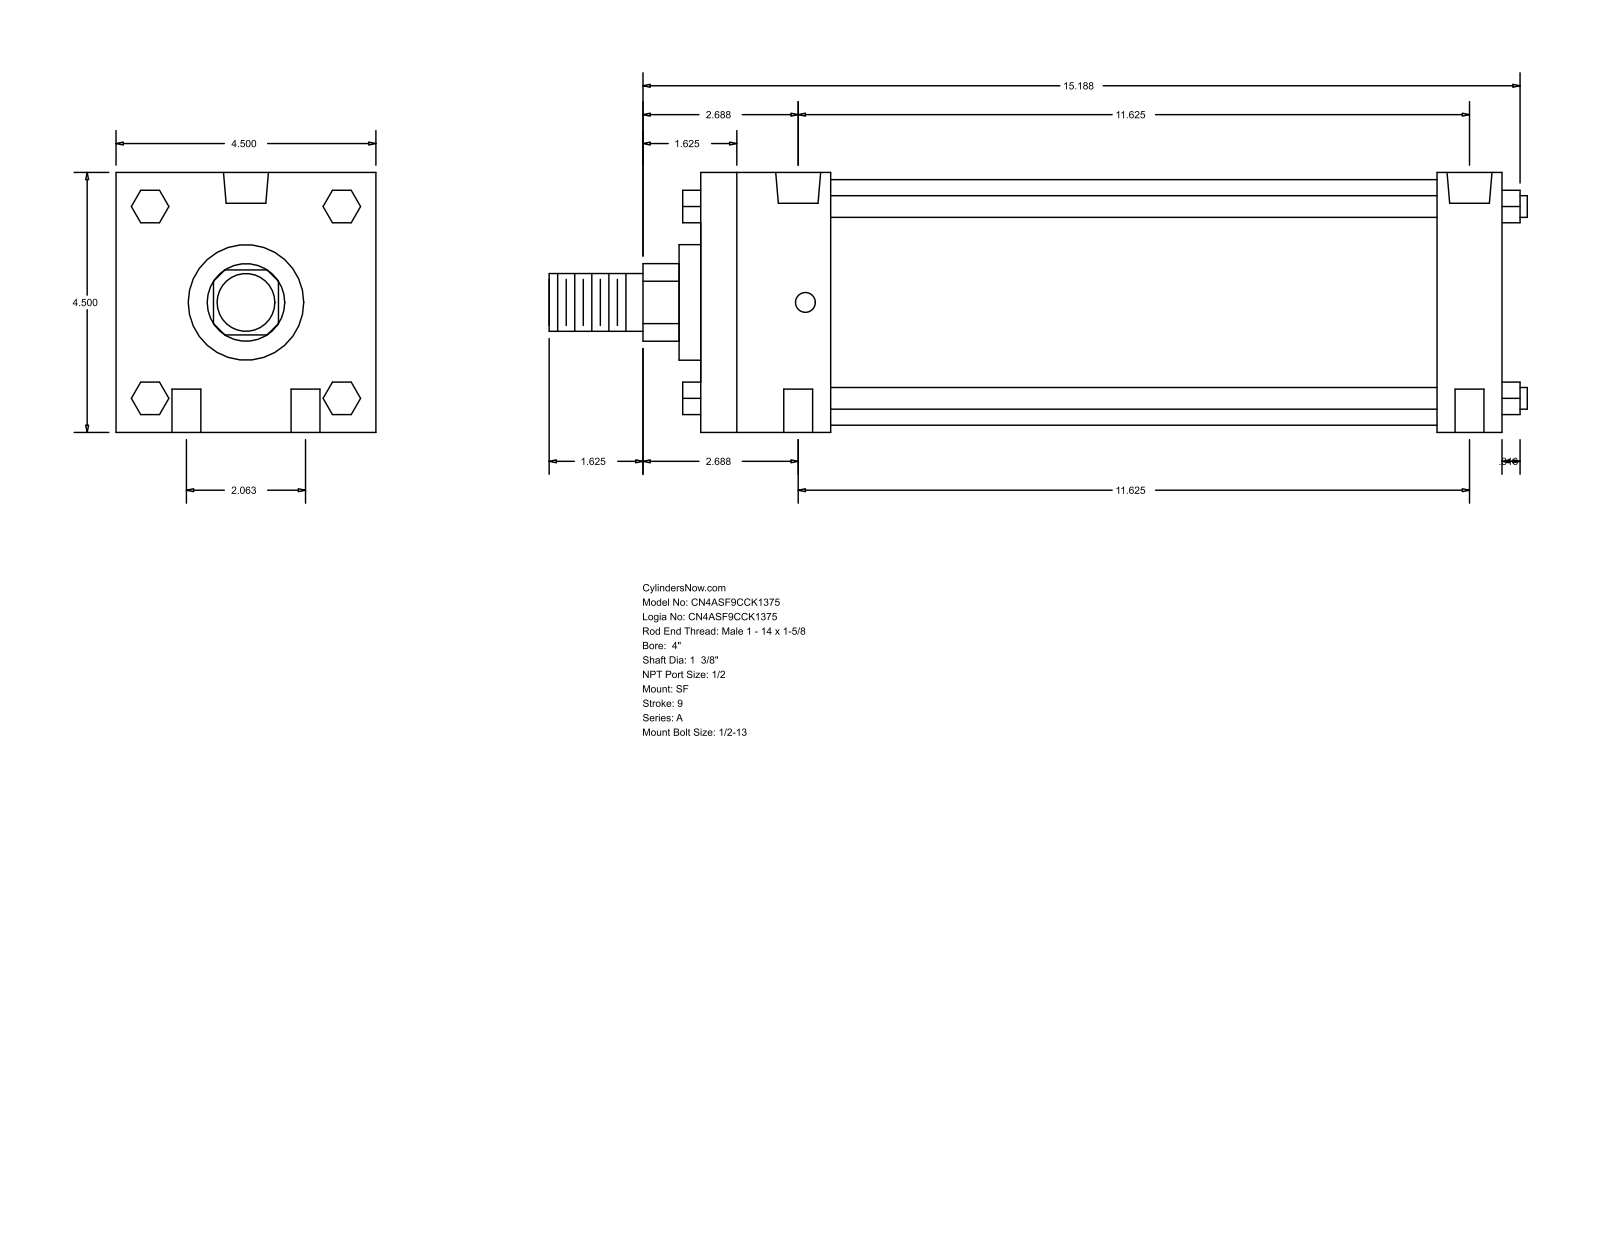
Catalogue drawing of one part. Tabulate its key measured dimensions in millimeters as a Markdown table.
| quantity | value |
| --- | --- |
| part name | A_SF__0400_1.375 |
| STEP written by | GSSL Pune (CONFIG_CONTROL_DESIGN) |
| units | millimeters |
| bodies | 0 solids, 124 faces (94 planar, 30 cylindrical, 0 other) |
| overall size | 430.21 × 114.3 × 114.3 |
| round holes (diameter × count) | 12.7 × 4, 8.73 × 2, 19.77 × 2 |
| round bosses / shafts (diameter × count) | 9.53 × 4, 107.95 × 1, 50.8 × 1, 34.92 × 1, 25.4 × 1 |
| partial cylindrical surfaces (radius × count) | 17.06 × 1 |
| main face-to-face distances | 114.3, 352.42, 57.15, 323.85, 28.57, 266.7, 295.27, 66.67, 14.29, 9.52 |
| hole center spacings | 26.19, 296.44, 295.28, 52.38, 299.89, 288.92 |
